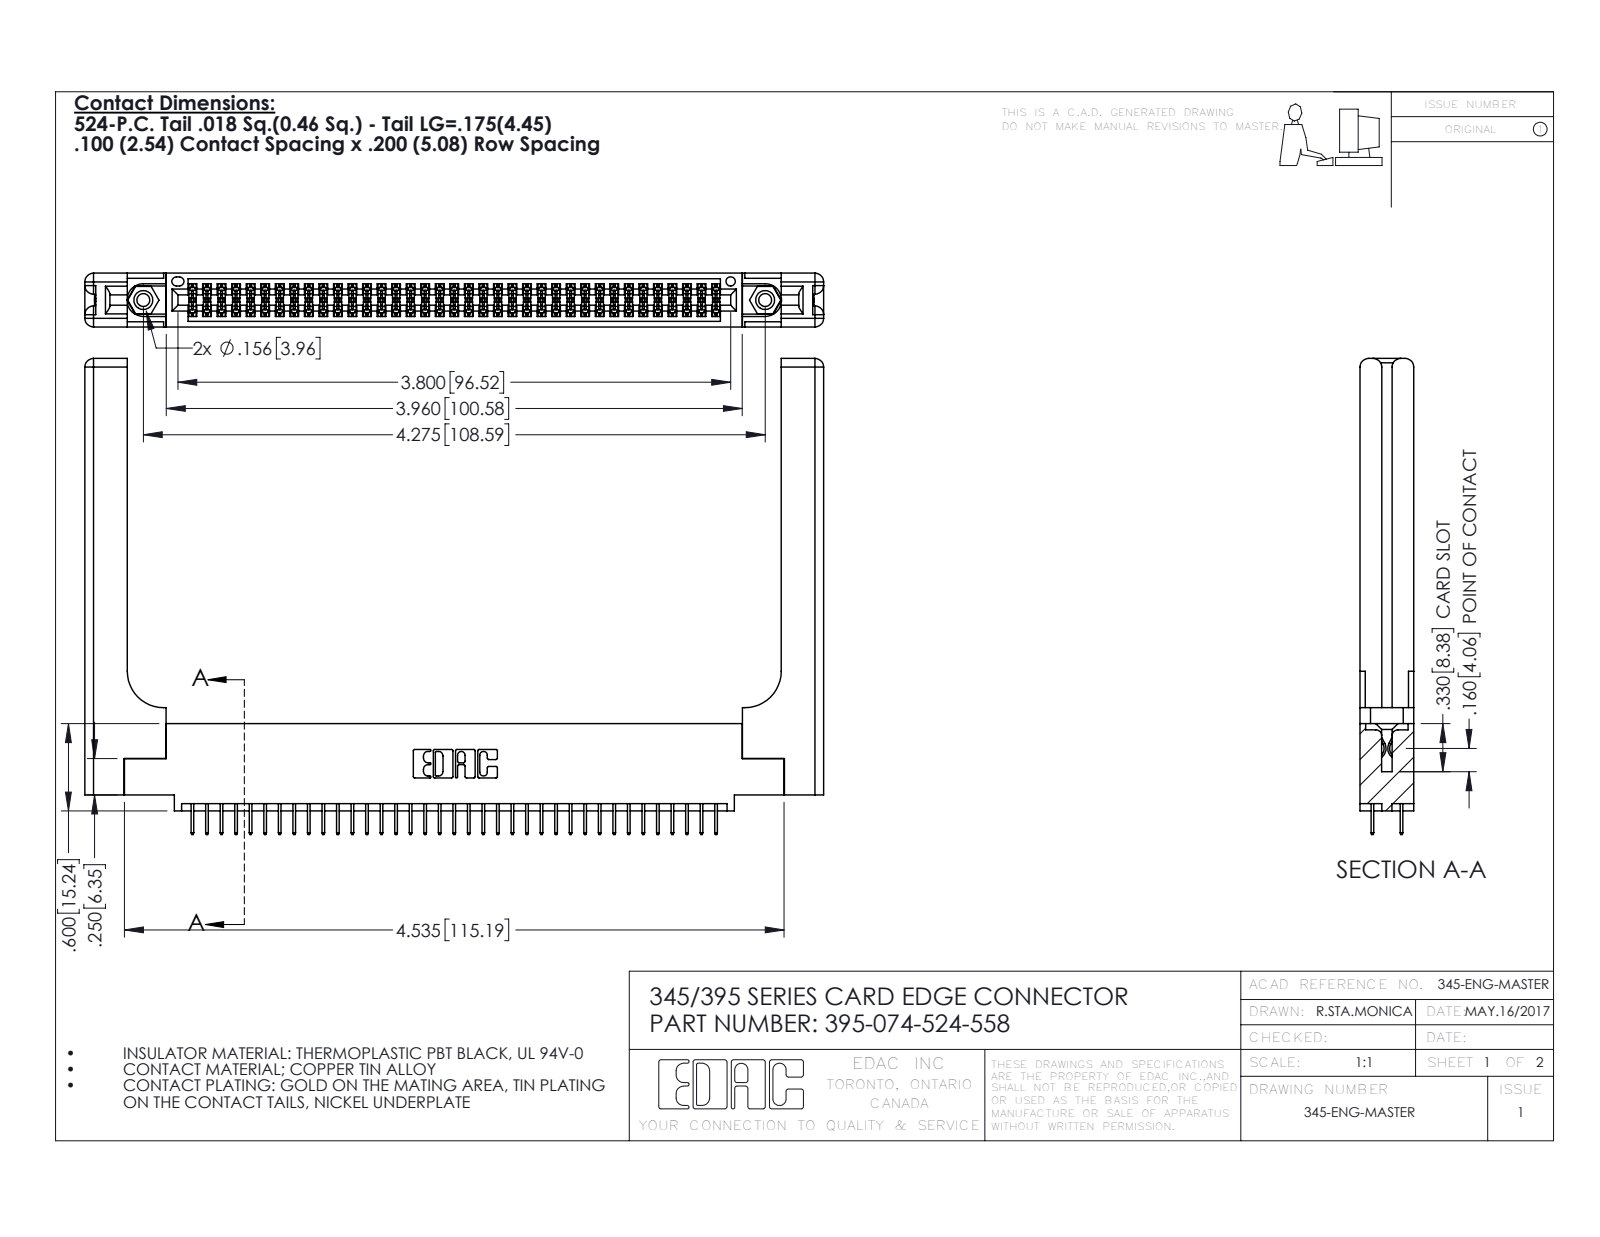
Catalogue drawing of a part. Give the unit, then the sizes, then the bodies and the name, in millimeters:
Units: millimetres
Overall size (bounding box): 129 × 83.1 × 9.4
Round holes (diameter × count): ⌀2.3 ×2, ⌀3.2 ×2, ⌀4 ×2, ⌀1.6 ×1
Round bosses / shafts (diameter × count): ⌀3.9 ×2
Partial cylindrical surfaces — rounded edges, fillets, slot ends (radius × count): R0.2 ×111, R0.3 ×22, R1.5 ×16, R0.2 ×6, R0.8 ×6, R0.7 ×3, R0.4 ×2, R0.5 ×2
Main face-to-face distances: 9.4, 1.8, 7.6, 5.1, 2.5, 6.9, 0.6, 5.7, 3.8, 3.8
Hole centre spacings: 6.9, 102.6, 108.6
Volume: 20 780 mm³ · Surface area: 22 940 mm²
Bodies: 79 solids, 4382 faces (3118 planar, 1204 cylindrical, 60 other)
Part name (STEP PRODUCT): 345 Part_0.110 Offset - 0.156 Dia-TH; 345-220-058_345-220-058; 345-292-001_345-293-124; 345-250-001_345-250-001-102 (+1 more)
STEP written by: SolidWorks 2016 (CONFIG_CONTROL_DESIGN)
